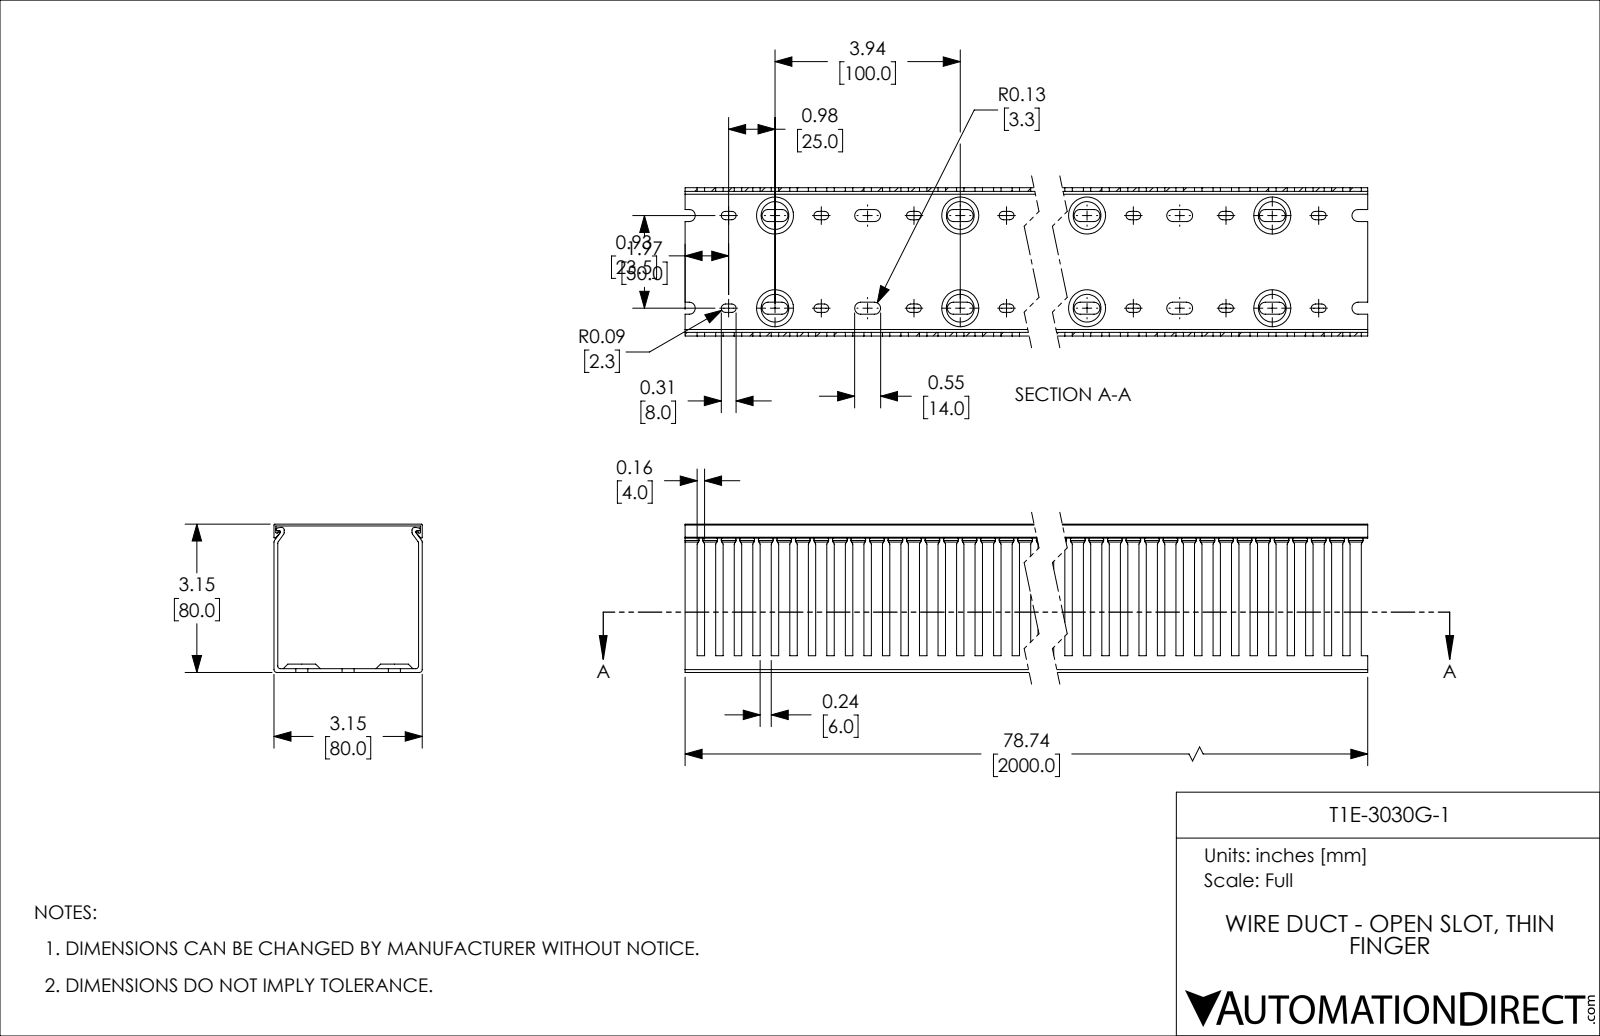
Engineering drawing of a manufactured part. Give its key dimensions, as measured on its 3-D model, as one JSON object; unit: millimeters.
{"part_name": "T1E-3030W-1", "step_written_by": "SolidWorks 2021 (CONFIG_CONTROL_DESIGN)", "units": "millimeters", "bodies": {"solids": 2, "faces": 1573, "planar": 762, "cylindrical": 731, "other": 80}, "overall_size": [2000, 80, 80], "volume_mm3": 1134000, "surface_area_mm2": 1334000, "partial_cylinders_radius": [[3.25, 200], [2.25, 160], [1.5, 12], [0.5, 8], [0.75, 6]], "face_to_face_distances": [2, 78, 80, 1, 79, 77, 76, 4.5, 74.5, 5.5]}
